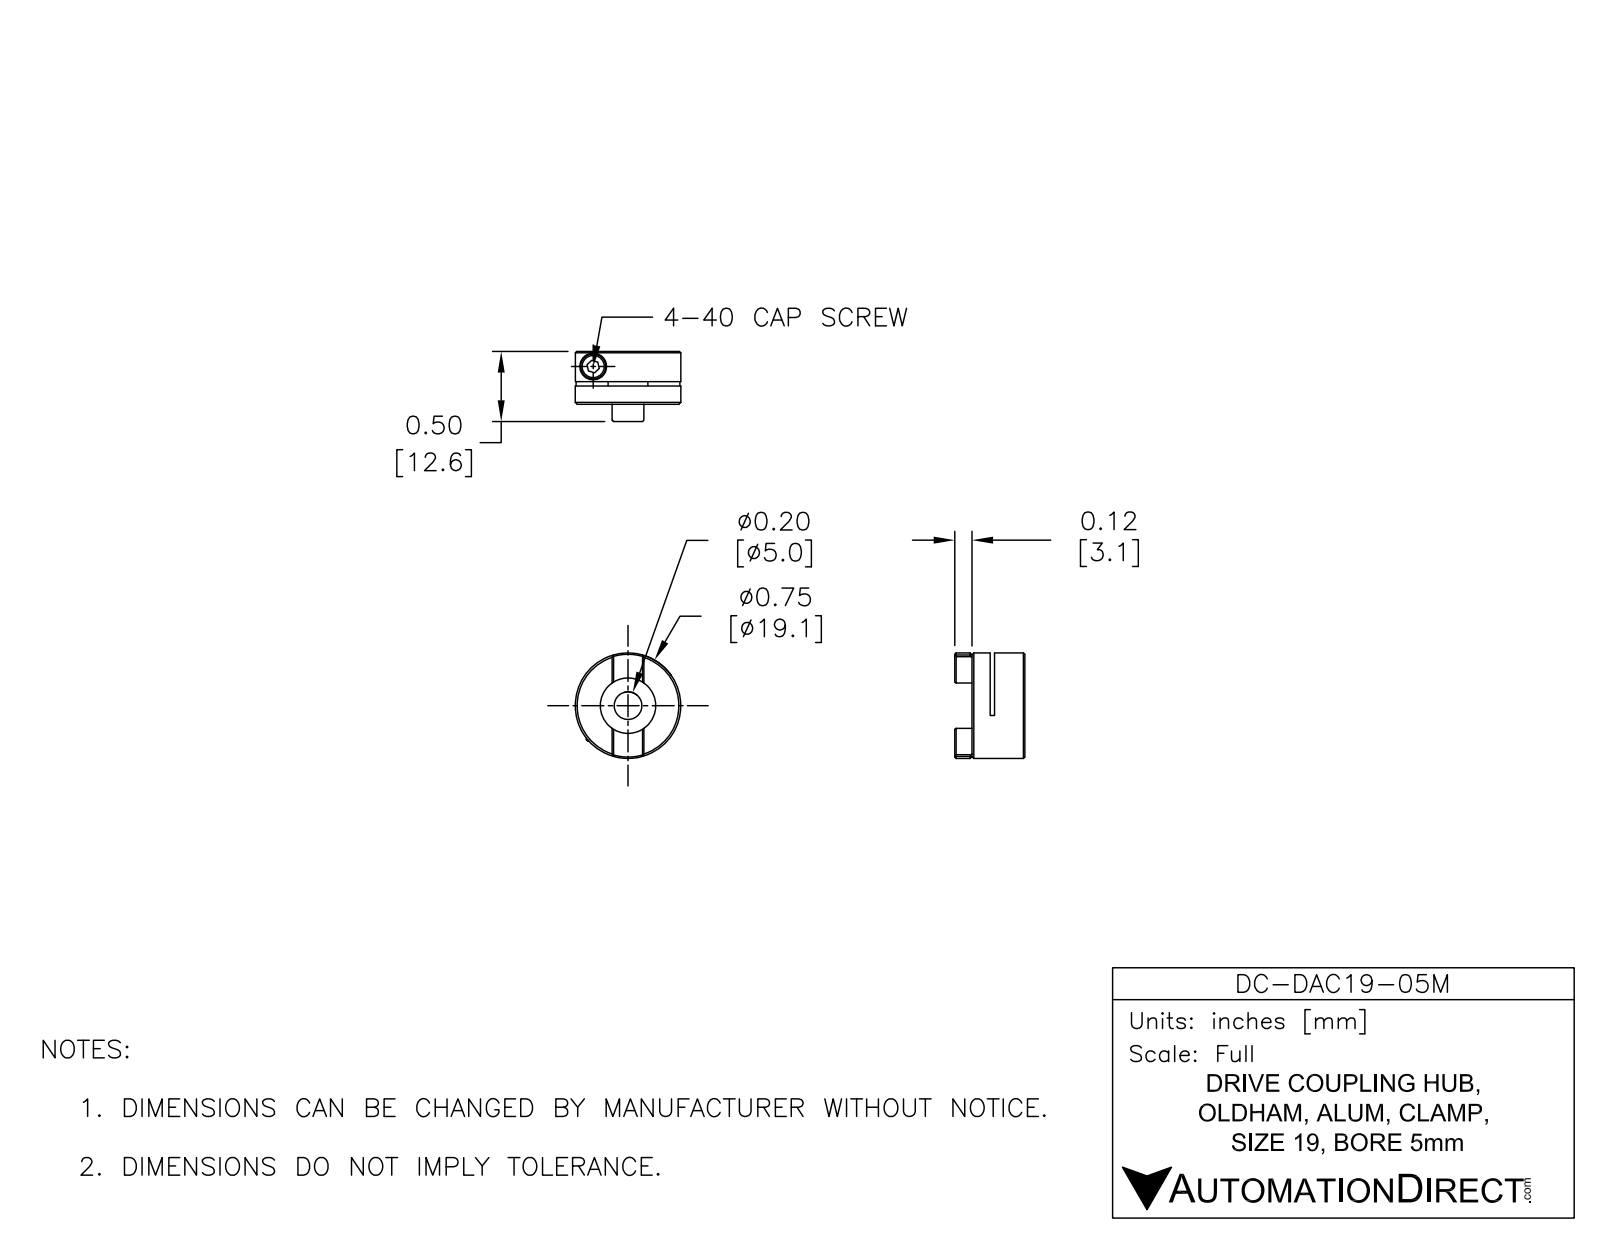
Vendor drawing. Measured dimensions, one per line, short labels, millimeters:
name: DC-DAC19-05M
written by: SolidWorks 2015 (AUTOMOTIVE_DESIGN)
unit: mm
bodies: 1 solid, 55 faces (29 planar, 18 cylindrical, 8 other)
size: 19.05 × 19.05 × 12.65
volume: 2 344 mm³; area: 1 841 mm²
holes: 1× ⌀2.01, 1× ⌀2.9, 1× ⌀4.83, 1× ⌀5, 1× ⌀10
bosses: 1× ⌀19.05
rounds: 1× R25.4
face distances: 6.25, 5.46, 0.79, 9.54, 4.08, 3.29, 9.03, 3.57, 2.78, 0.51
